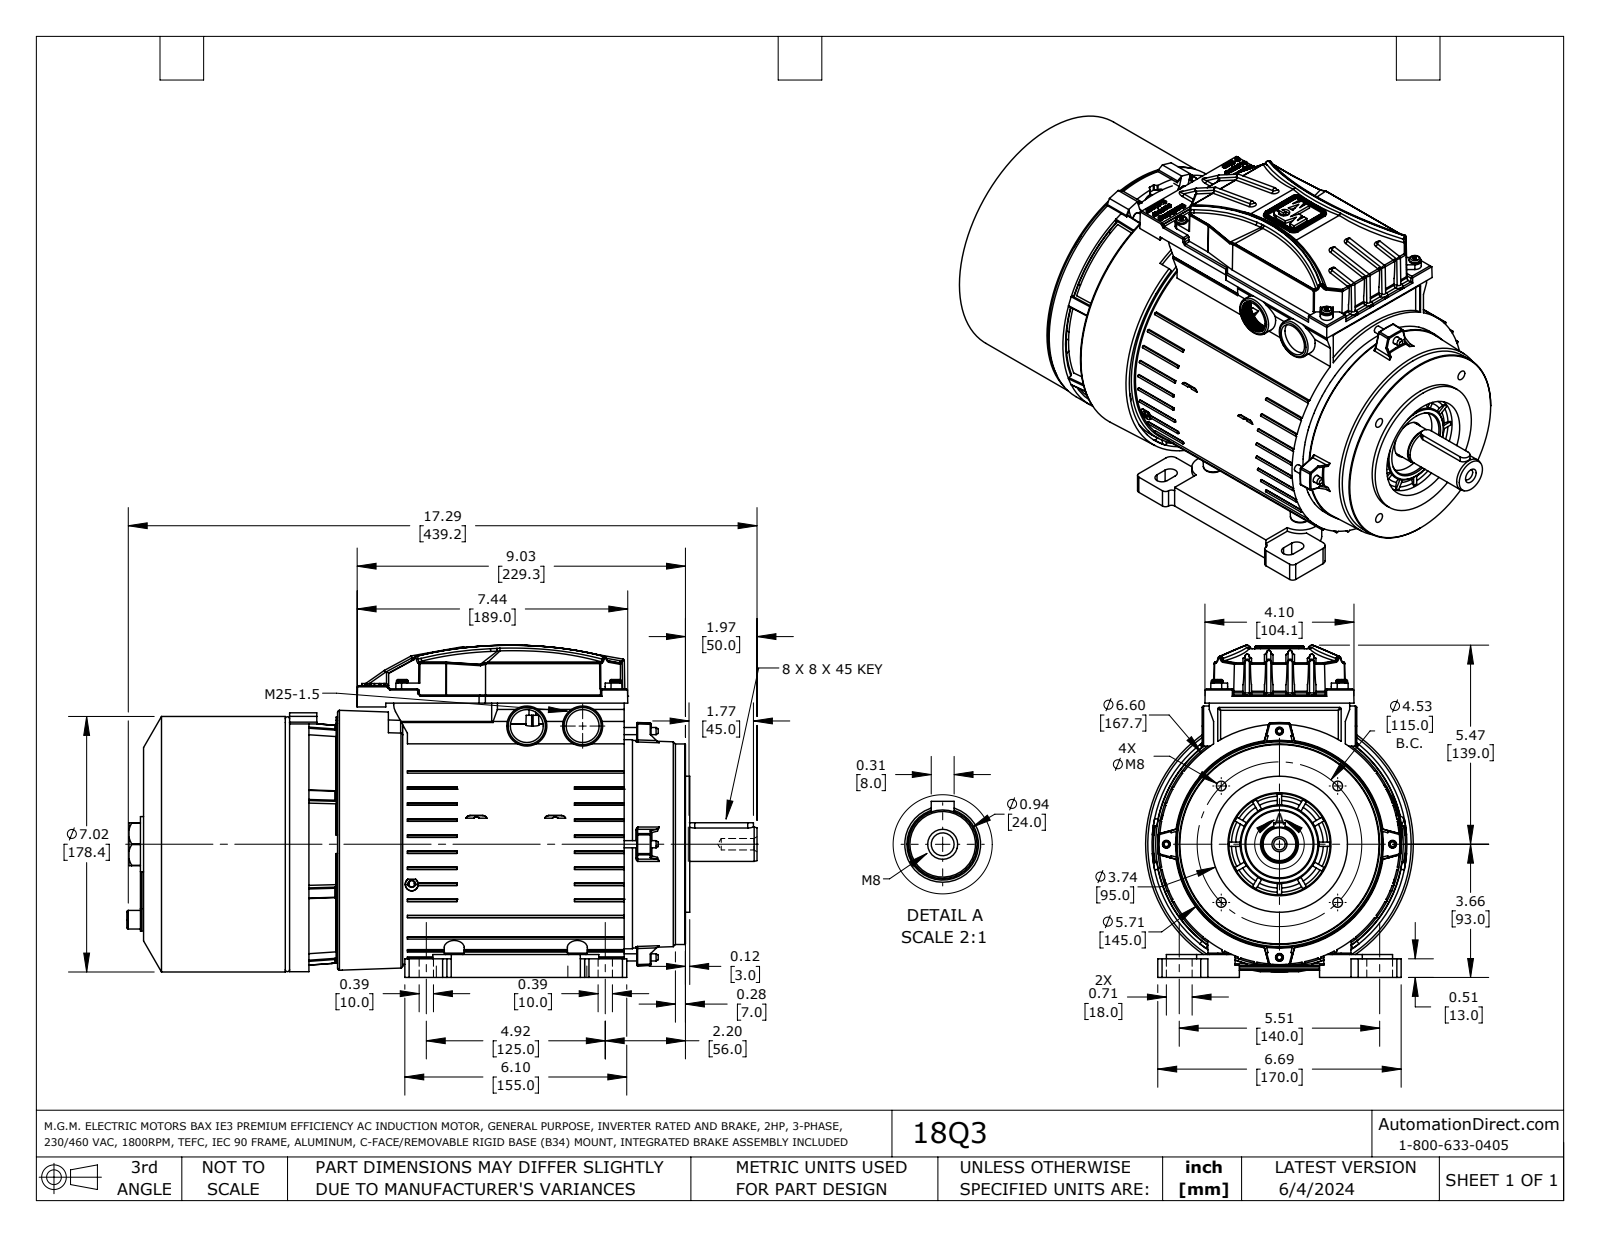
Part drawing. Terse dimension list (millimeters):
name: 18Q3
written by: SolidWorks 2021 (AUTOMOTIVE_DESIGN)
unit: mm
bodies: 17 solids, 3456 faces (1493 planar, 813 cylindrical, 1150 other)
size: 440.2 × 232 × 187
volume: 8 385 000 mm³; area: 733 500 mm²
holes: 13× ⌀3.3, 5× ⌀2.5, 4× ⌀3.8, 4× ⌀4.5, 4× ⌀5.5, 4× ⌀6.8, 4× ⌀25, 2× ⌀3, 2× ⌀6.5, 2× ⌀23, 1× ⌀8, 1× ⌀12
bosses: 6× ⌀5, 6× ⌀3.5, 4× ⌀13.3, 4× ⌀8, 3× ⌀7, 2× ⌀28, 2× ⌀11.5, 1× ⌀180
rounds: 56× R0.2, 47× R1.5, 36× R0.6, 26× R1, 24× R0.1, 22× R0.5, 22× R0.8, 18× R3
face distances: 1.3, 16.5, 21.3, 20, 37.8, 36.5, 136.8, 135.5, 115.5, 99
hole spacings: 12, 55.9, 126.4, 20.8, 73.7, 46, 49.8, 55.6
